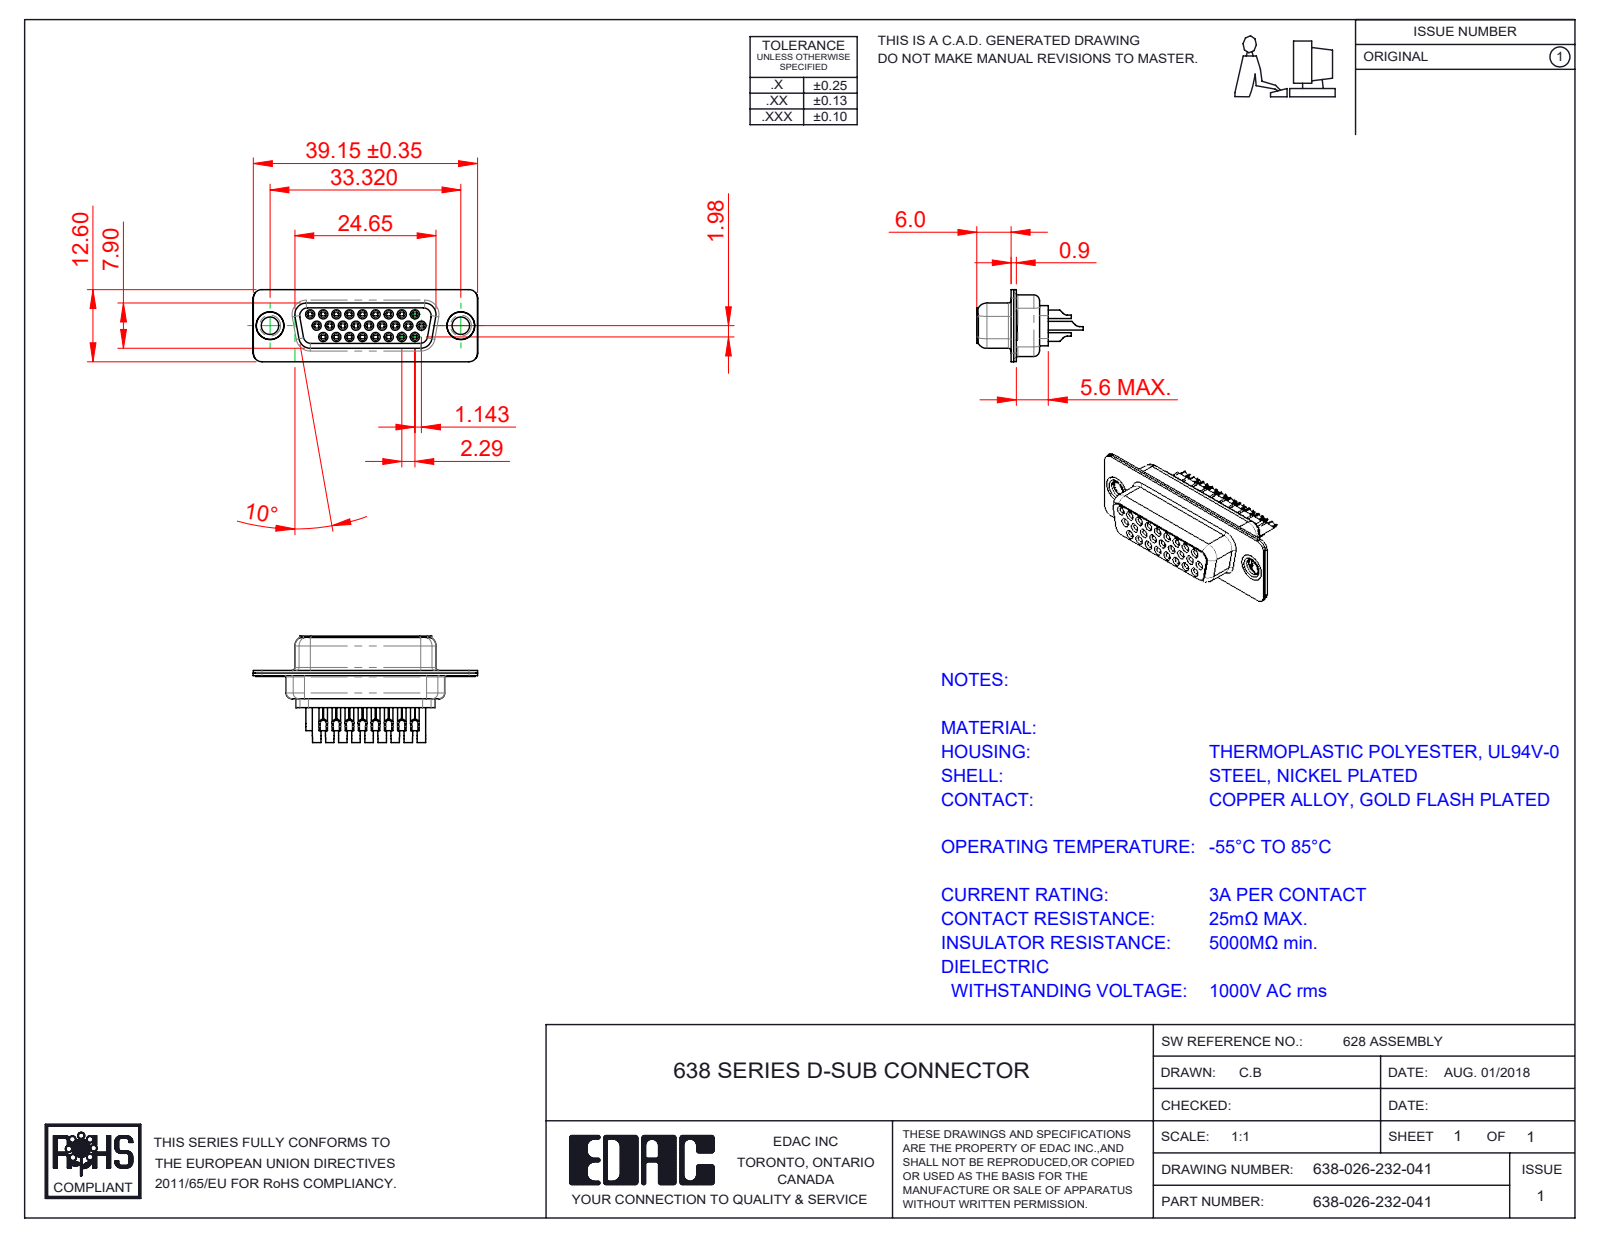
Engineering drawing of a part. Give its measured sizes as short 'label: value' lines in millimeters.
name: 638 Contact Row 3_32; 638 Thru Hole Rivet; 638-026-232-041; 638 Shell Rear_26 Contacts (+4 more)
written by: SolidWorks 2020 (CONFIG_CONTROL_DESIGN)
unit: mm
bodies: 31 solids, 2567 faces (613 planar, 771 cylindrical, 1183 other)
size: 39.19 × 18.6 × 12.6
volume: 2 183 mm³; area: 8 622 mm²
holes: 26× ⌀0.8, 26× ⌀1, 26× ⌀1.1, 26× ⌀1.6, 26× ⌀1.7, 26× ⌀1.8, 2× ⌀3.05, 2× ⌀4, 2× ⌀4.05, 2× ⌀4.85
bosses: 26× ⌀2, 26× ⌀1.5, 26× ⌀1.2, 2× ⌀5, 2× ⌀4.95, 2× ⌀4.8, 2× ⌀3.55
rounds: 20× R1.5, 18× R0.28, 12× R2, 8× R1.55, 7× R1, 5× R1.35, 4× R0.25, 4× R0.5
face distances: 0.45, 0.4, 1.43, 8.88, 0.9, 6.6, 1.4, 2.28, 7.05, 0.85
hole spacings: 3.96, 2.28, 4.57, 6.05, 2.29, 8.24, 6.86, 10.48
